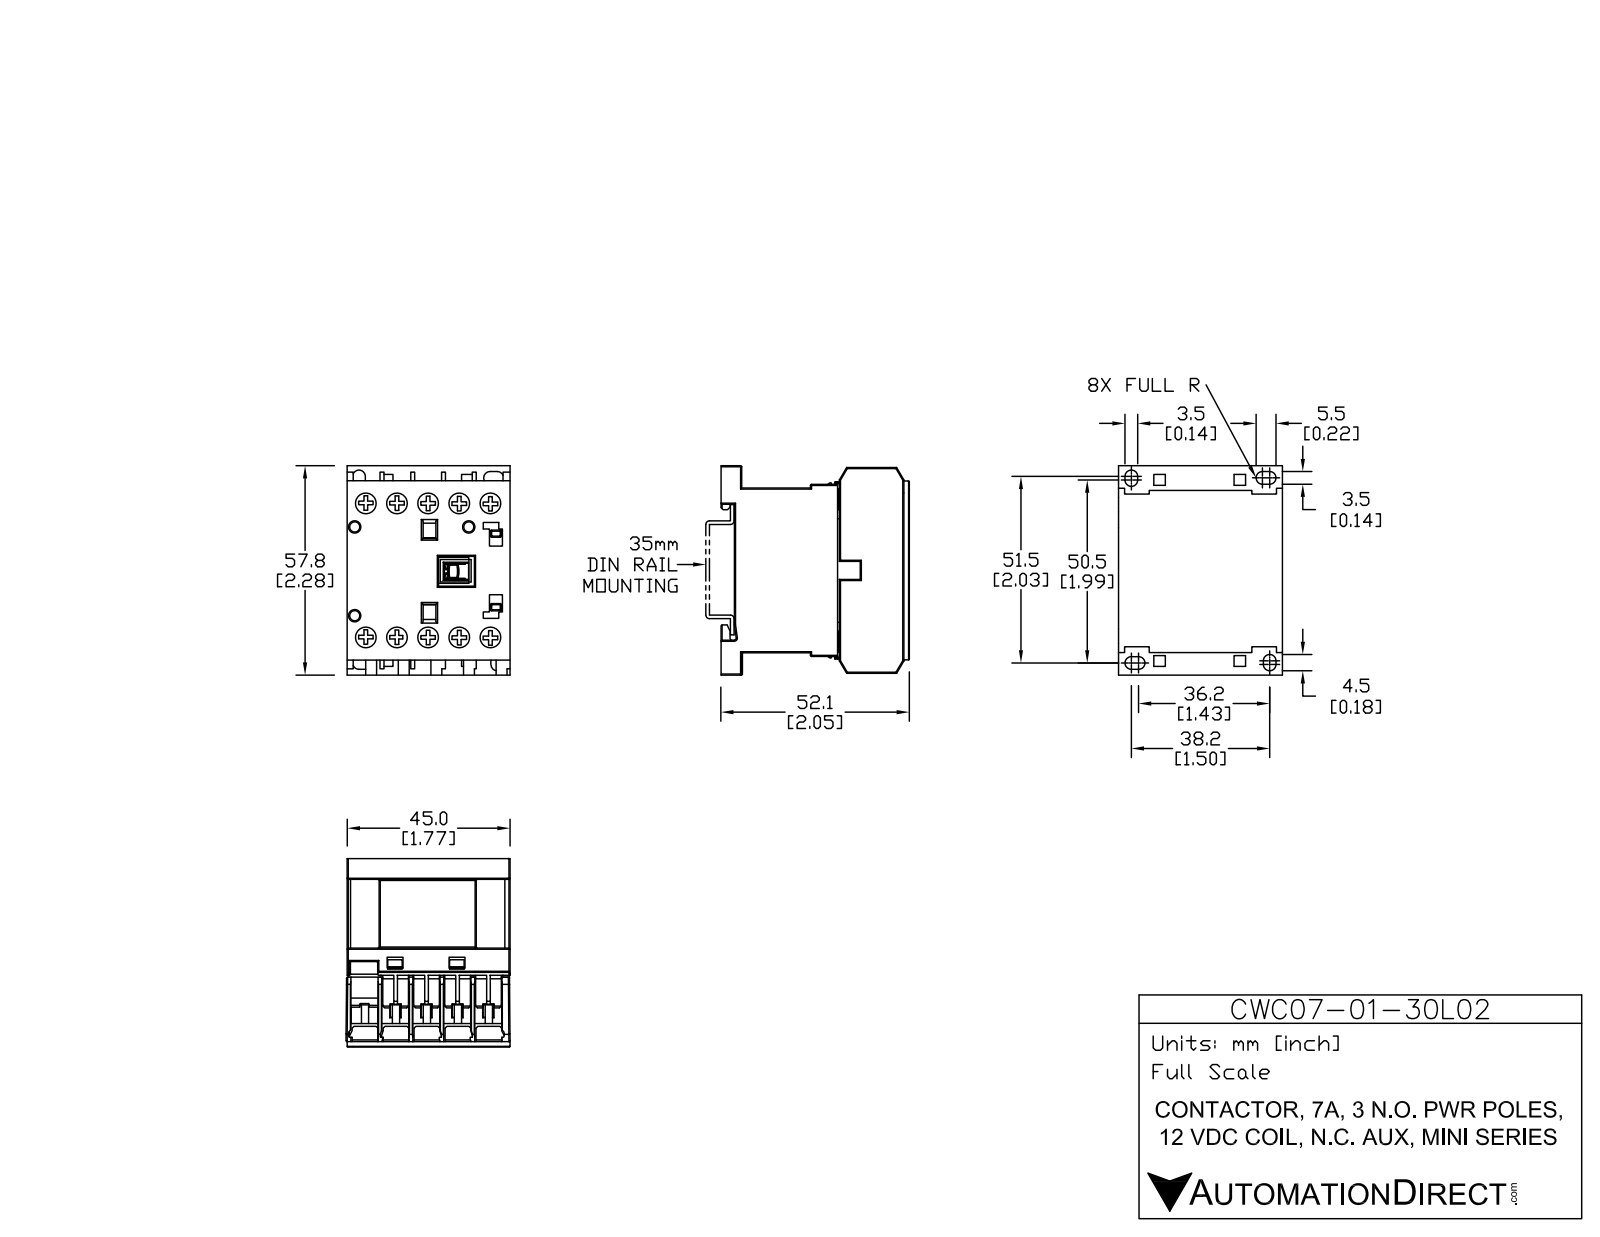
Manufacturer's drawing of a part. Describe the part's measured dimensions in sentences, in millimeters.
The part is named "CWC07-01-30L02". Its 3-D file was written by "SolidWorks 2013 (AUTOMOTIVE_DESIGN)". It is 15 solids with 535 faces: 445 planar, 90 cylindrical and 0 other. Overall it measures 58.04 by 52.12 by 45.75 millimeters. Its volume is 97 133 cubic millimeters and its surface area 30 437 square millimeters. Round holes: 10 of diameter 6.2, 3 of diameter 2.8. Round bosses or shafts: 10 of diameter 5.9. Partial cylindrical surfaces (rounded edges, fillets, slot ends): 20 of radius 0.3, 6 of radius 1.72, 2 of radius 1.73, 1 of radius 0.32, 1 of radius 0.42, 1 of radius 0.55. The main face-to-face distances are 8.25, 45.5, 1.25, 16.5, 9.5, 5.5, 17.75, 5.13, 10.63, 7. The hole center spacings are 8.55, 37.94, 17.1, 40.72, 36.96, 25.65, 44.99, 6.91.
